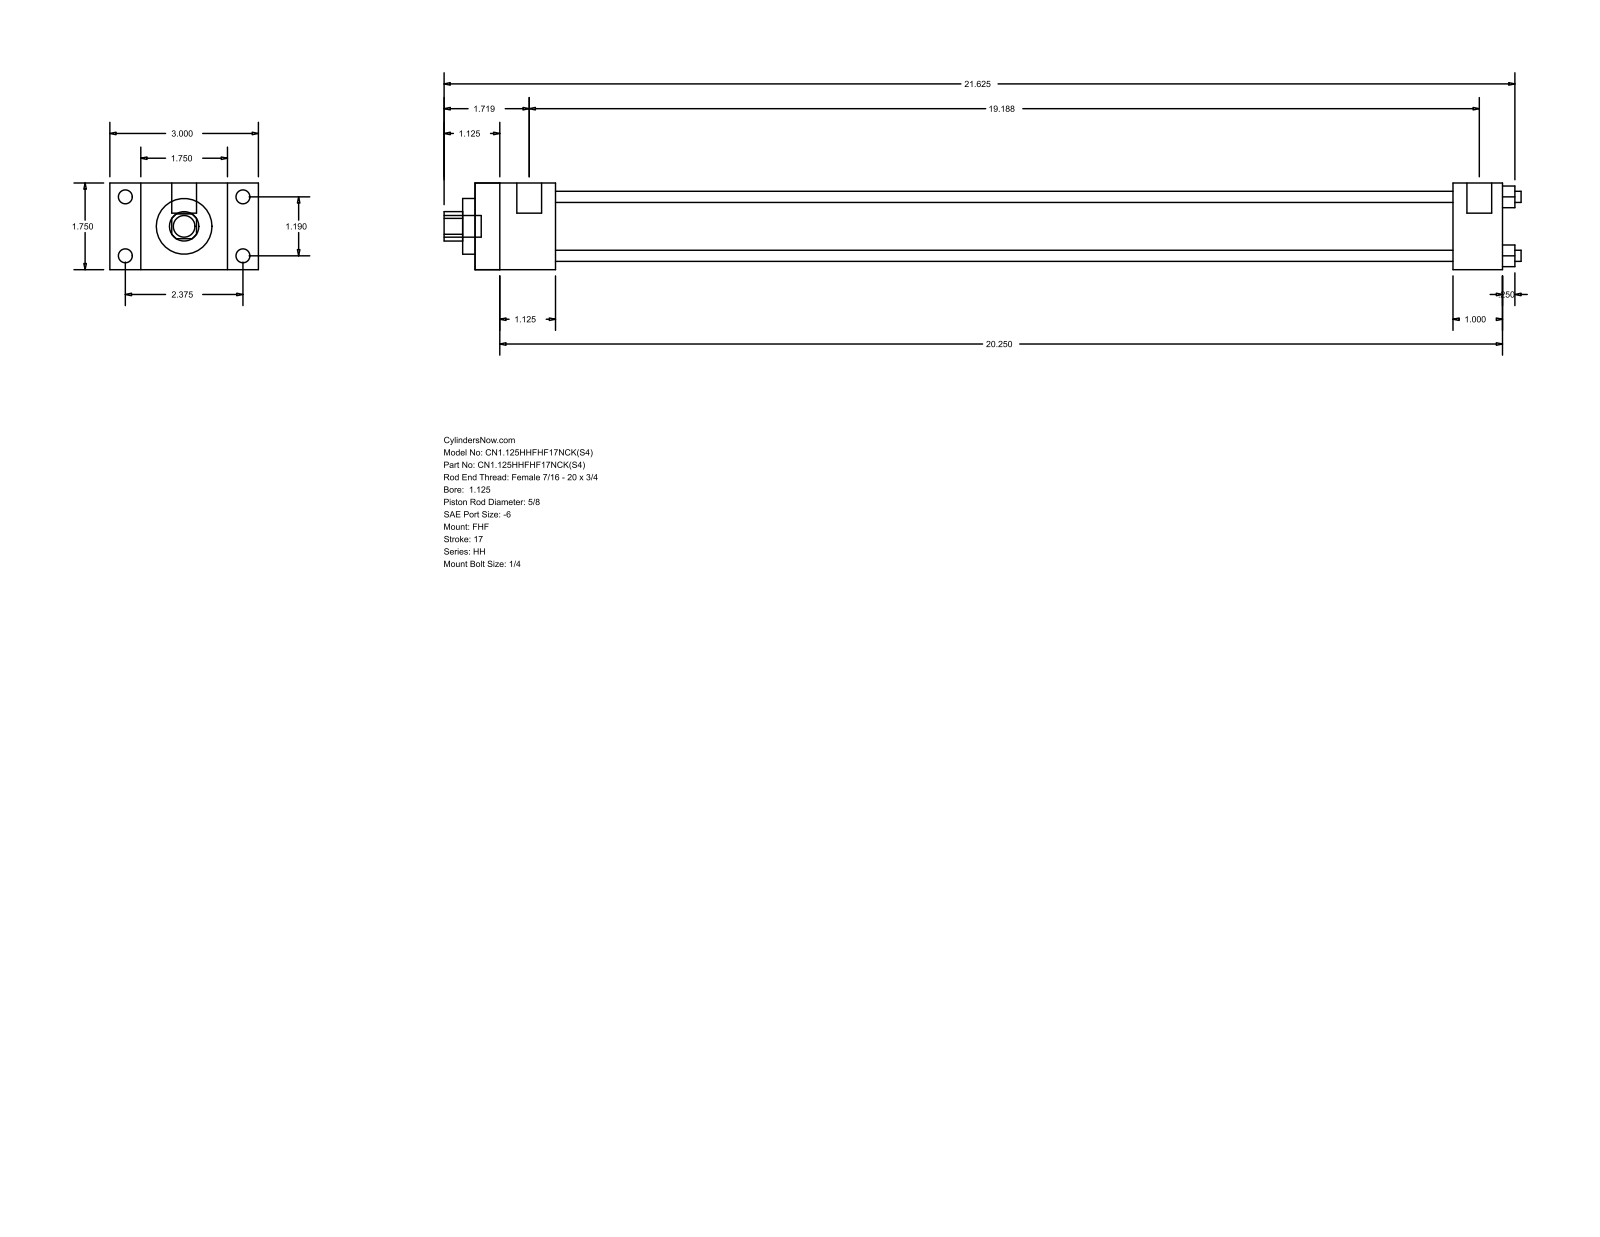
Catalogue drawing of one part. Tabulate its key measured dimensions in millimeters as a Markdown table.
| quantity | value |
| --- | --- |
| part name | HH_FHF__0112_0.625 |
| STEP written by | GSSL Pune (CONFIG_CONTROL_DESIGN) |
| units | millimeters |
| bodies | 0 solids, 88 faces (60 planar, 28 cylindrical, 0 other) |
| overall size | 552.45 × 76.2 × 44.45 |
| round holes (diameter × count) | 5.71 × 4, 15.88 × 1, 28.57 × 1, 34.92 × 1 |
| round bosses / shafts (diameter × count) | 7.14 × 4, 5.56 × 4, 12.7 × 2, 11.11 × 1 |
| partial cylindrical surfaces (radius × count) | 7.54 × 1 |
| main face-to-face distances | 44.46, 15.87, 60.33, 41.27, 76.2, 527.04, 485.77, 501.64, 460.37, 25.4 |
| hole center spacings | 21.37, 30.22, 42.74 |
